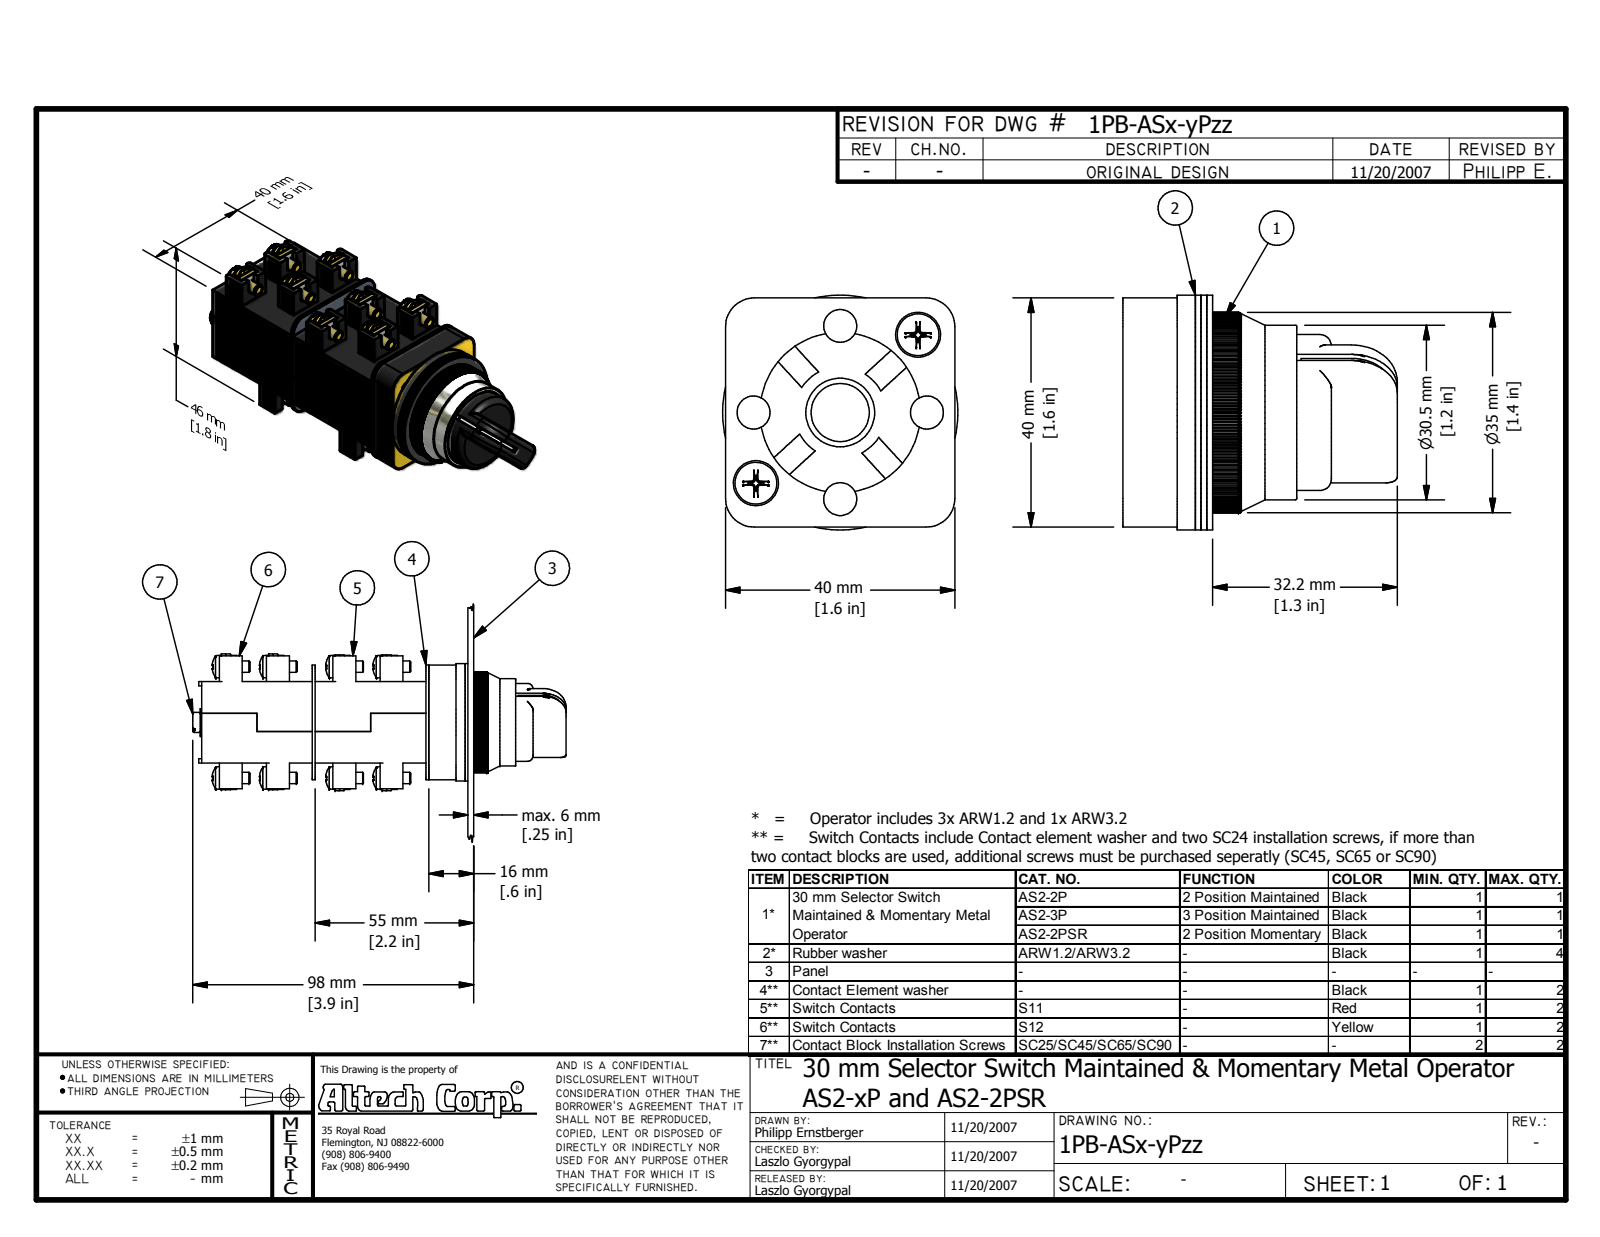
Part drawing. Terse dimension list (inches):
name: ASx-xPxx; base; rubber_gasket_3mm; rubber_gasket_1mm (+2 more)
written by: Autodesk Inventor 2008 (AUTOMOTIVE_DESIGN)
unit: in
bodies: 8 solids, 787 faces (484 planar, 248 cylindrical, 55 other)
size: 1.884 × 1.614 × 1.614
volume: 2.362 in³; area: 33.59 in²
holes: 2× ⌀0.226, 1× ⌀0.138, 1× ⌀0.309, 1× ⌀0.472, 1× ⌀0.965, 1× ⌀1.083, 1× ⌀1.181, 1× ⌀1.201, 1× ⌀1.22
bosses: 2× ⌀0.287, 2× ⌀0.123, 1× ⌀1.614, 1× ⌀1.073, 1× ⌀0.945, 1× ⌀0.4, 1× ⌀0.138
rounds: 4× R0.079, 4× R0.197, 1× R0.433, 1× R0.497, 1× R0.522, 1× R0.551, 1× R0.689
face distances: 0.039, 0.079, 0.498, 0.124, 0.203, 0.163, 0.537, 0.577, 0.616, 0.118
hole spacings: 0.596, 0.589, 0.756, 0.843, 1.271
